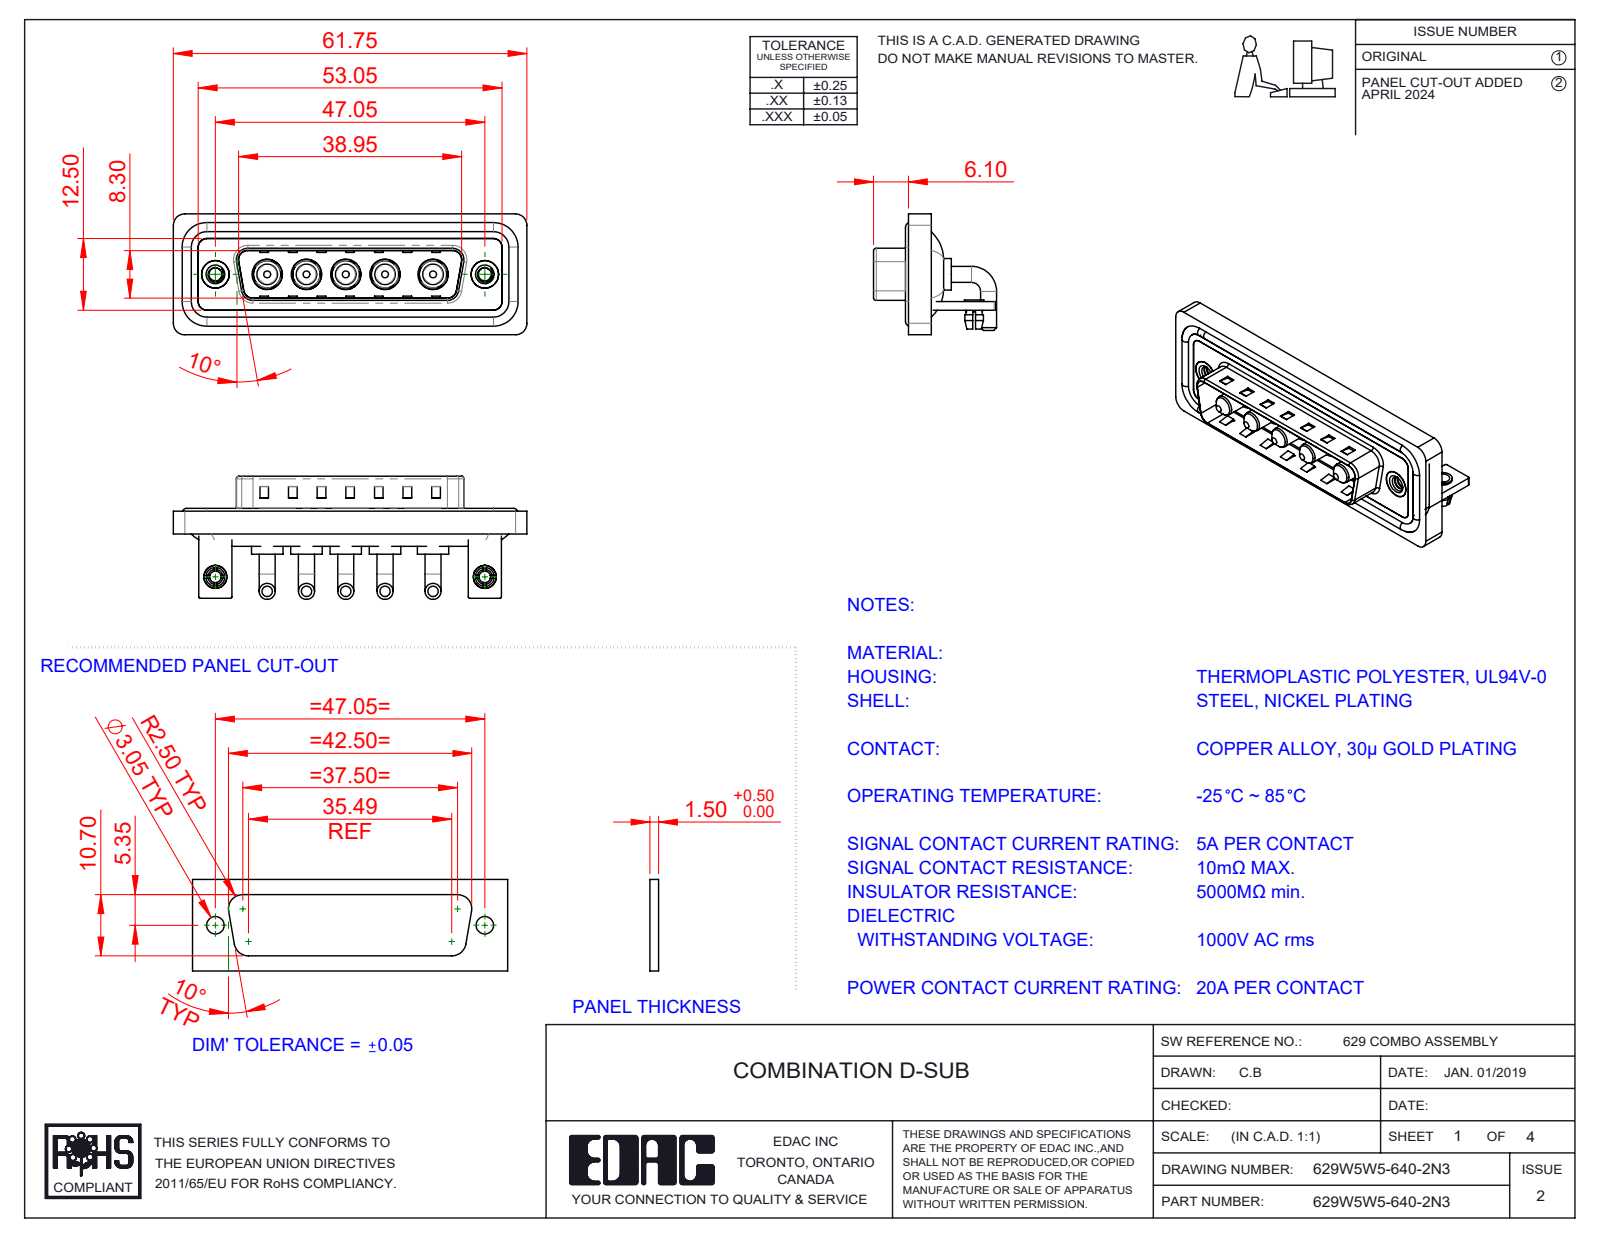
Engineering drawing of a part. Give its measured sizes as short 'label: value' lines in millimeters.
name: 629W5W5-640-2N3; 629Combo Stabilizer Bracket; 629Combo Threaded Rivet_3; 629Combo Waterproof Housing_25 Contacts (+5 more)
written by: SolidWorks 2023 (CONFIG_CONTROL_DESIGN)
unit: mm
bodies: 21 solids, 830 faces (327 planar, 343 cylindrical, 160 other)
size: 61.75 × 21.5 × 21.1
volume: 8 116 mm³; area: 13 069 mm²
holes: 5× ⌀4.85, 5× ⌀5.3, 2× ⌀2, 2× ⌀2.26, 2× ⌀2.5, 2× ⌀3.2, 2× ⌀4, 2× ⌀4.8, 2× ⌀5
bosses: 10× ⌀2.8, 5× ⌀5.5, 5× ⌀5.2, 5× ⌀4.75, 5× ⌀3.75, 5× ⌀3.6, 4× ⌀1.6, 2× ⌀4.9
rounds: 19× R2, 18× R1.5, 16× R0.25, 9× R0.5, 8× R1.6, 5× R2.1, 4× R0.6, 4× R0.65
face distances: 0.4, 1.5, 2.9, 0.8, 2.1, 1.1, 3.7, 4.5, 4.1, 1.2
hole spacings: 6.86, 13.73, 47.05, 6.85, 6.87, 8.37, 8.38, 9.04
